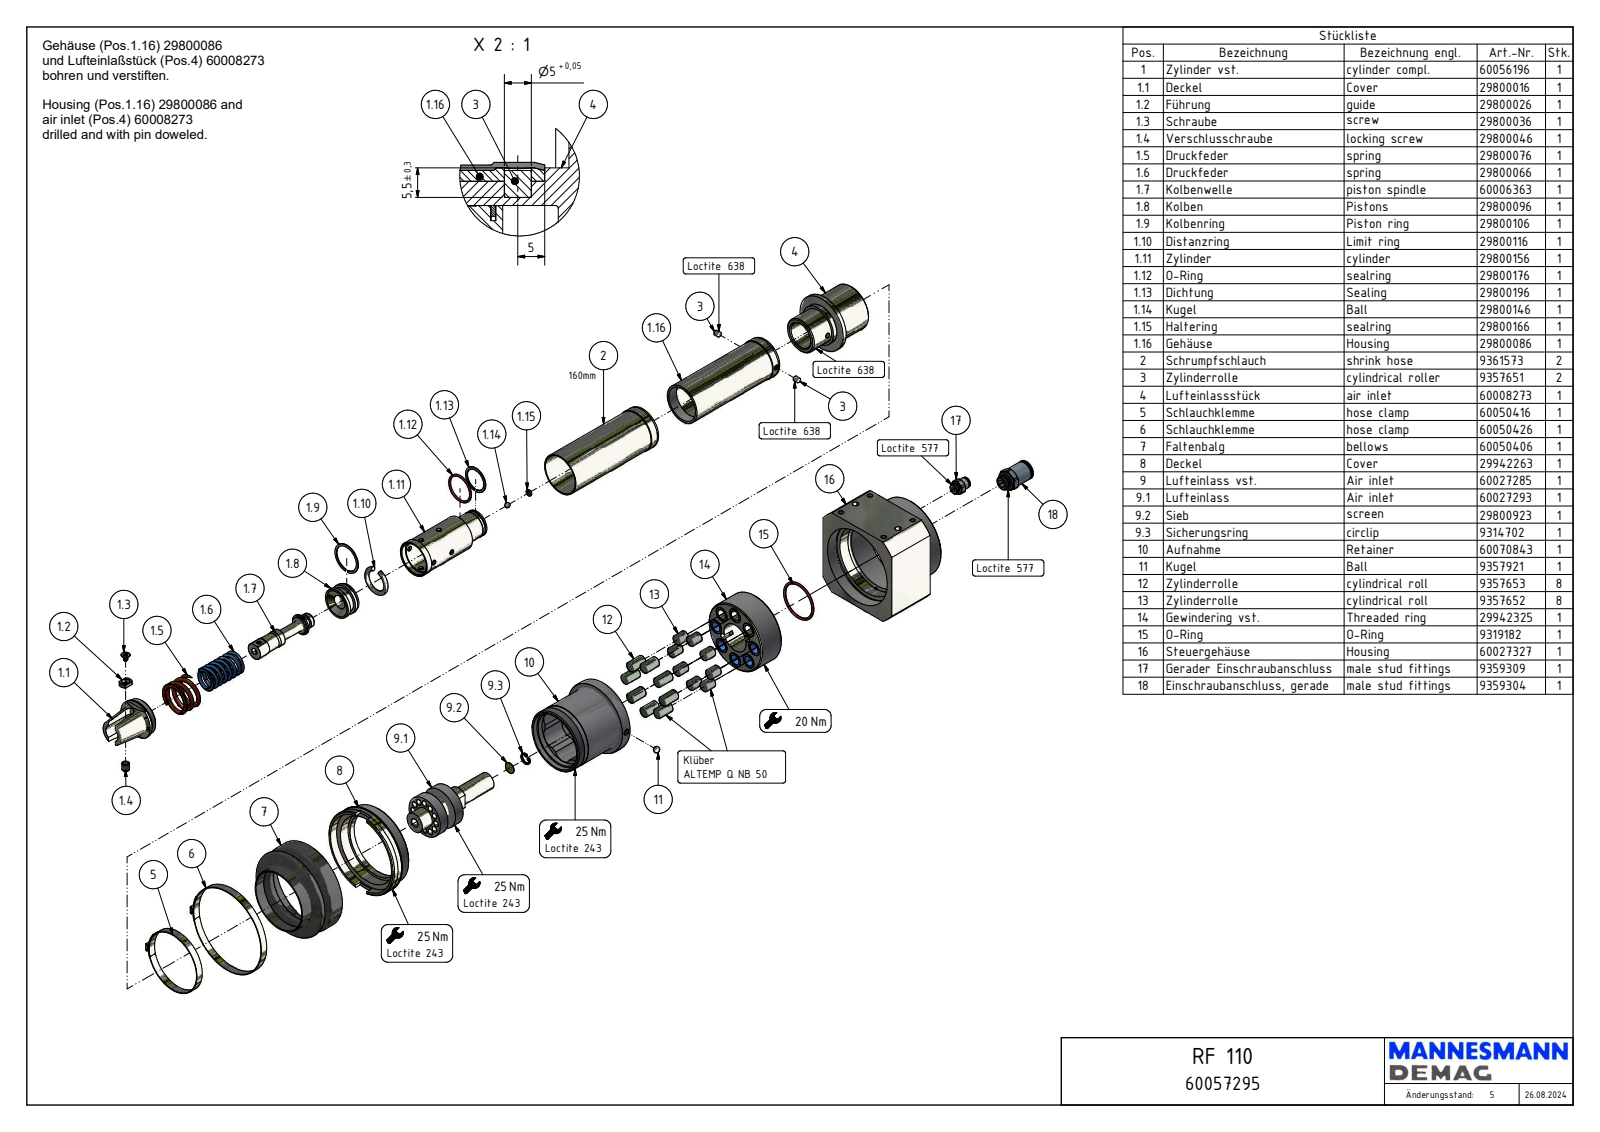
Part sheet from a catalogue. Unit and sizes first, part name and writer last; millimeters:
Units: millimetres
Overall size (bounding box): 285.55 × 93.71 × 90
Round holes (diameter × count): ⌀4.92 ×4, ⌀6 ×3, ⌀6 ×2, ⌀2.5 ×1, ⌀3.24 ×1, ⌀4 ×1, ⌀5 ×1, ⌀6.4 ×1, ⌀8.57 ×1, ⌀12 ×1, ⌀36 ×1, ⌀60 ×1
Round bosses / shafts (diameter × count): ⌀89.2 ×1, ⌀88 ×1, ⌀80 ×1, ⌀78.18 ×1, ⌀63.2 ×1, ⌀61.7 ×1, ⌀61 ×1, ⌀56.5 ×1
Partial cylindrical surfaces — rounded edges, fillets, slot ends (radius × count): R0.5 ×8, R1 ×8, R1.1 ×8, R1.4 ×4, R2 ×4, R2.96 ×1, R4.55 ×1, R6 ×1
Main face-to-face distances: 90, 20, 50.5, 70.5, 37, 87.5, 107.5, 105, 68, 17.5
Hole centre spacings: 19, 59.14, 56, 28.04, 33.02, 34.7, 38, 67.68
Volume: 845 998 mm³ · Surface area: 82 333 mm²
Bodies: 2 solids, 364 faces (150 planar, 130 cylindrical, 84 other)
Part name (STEP PRODUCT): RF 110_60057295
STEP written by: Autodesk Inventor 2024 (AUTOMOTIVE_DESIGN)
